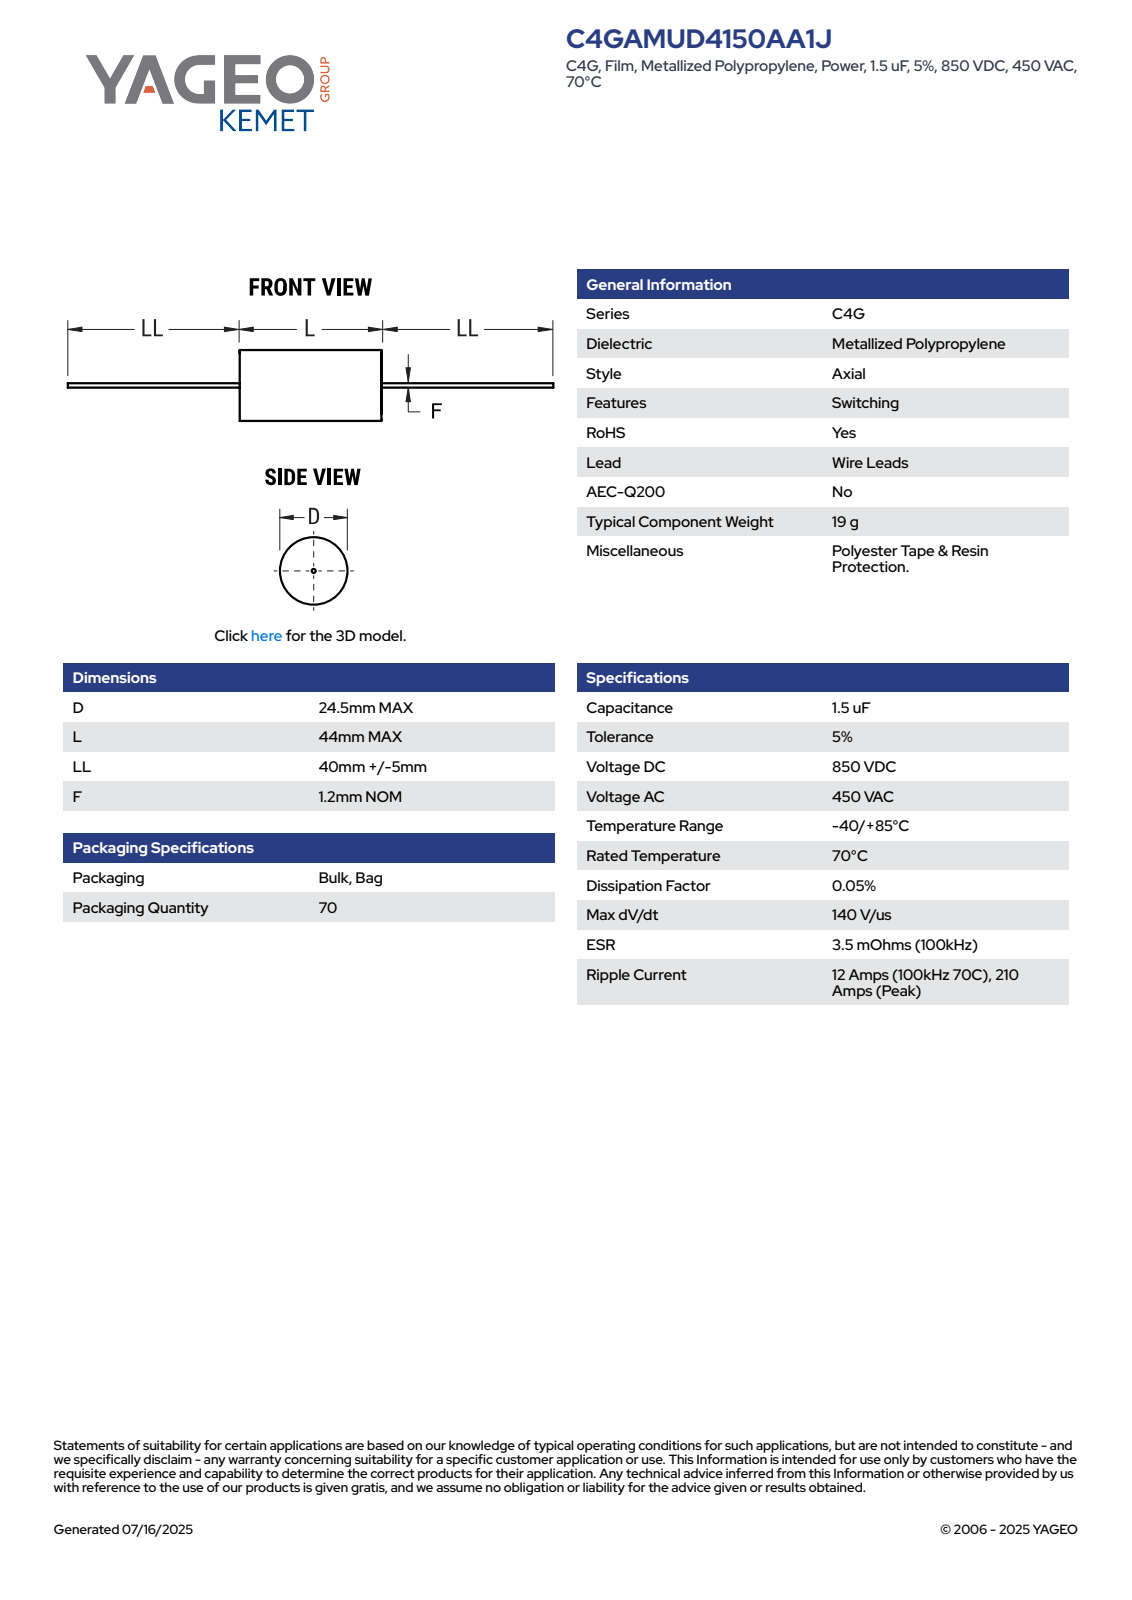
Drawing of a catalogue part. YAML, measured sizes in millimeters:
part_name: "CFP_ACWF_24.5X44_D24.5L44LL45F1.2"
step_written_by: "SolidWorks 2014 (AUTOMOTIVE_DESIGN)"
units: millimeters
bodies: {solids: 2, faces: 87, planar: 28, cylindrical: 28, other: 31}
overall_size: [134, 24.5, 24.5]
volume: 20845
surface_area: 5610
round_bosses_or_shafts:
  - {diameter: 24.5, count: 1}
  - {diameter: 1.2, count: 1}
partial_cylinders:
  - {radius: 12.24, count: 1}
face_to_face_distances: [44, 43.99, 44.99, 45, 88.99, 134, 89.01, 89, 45.01]
